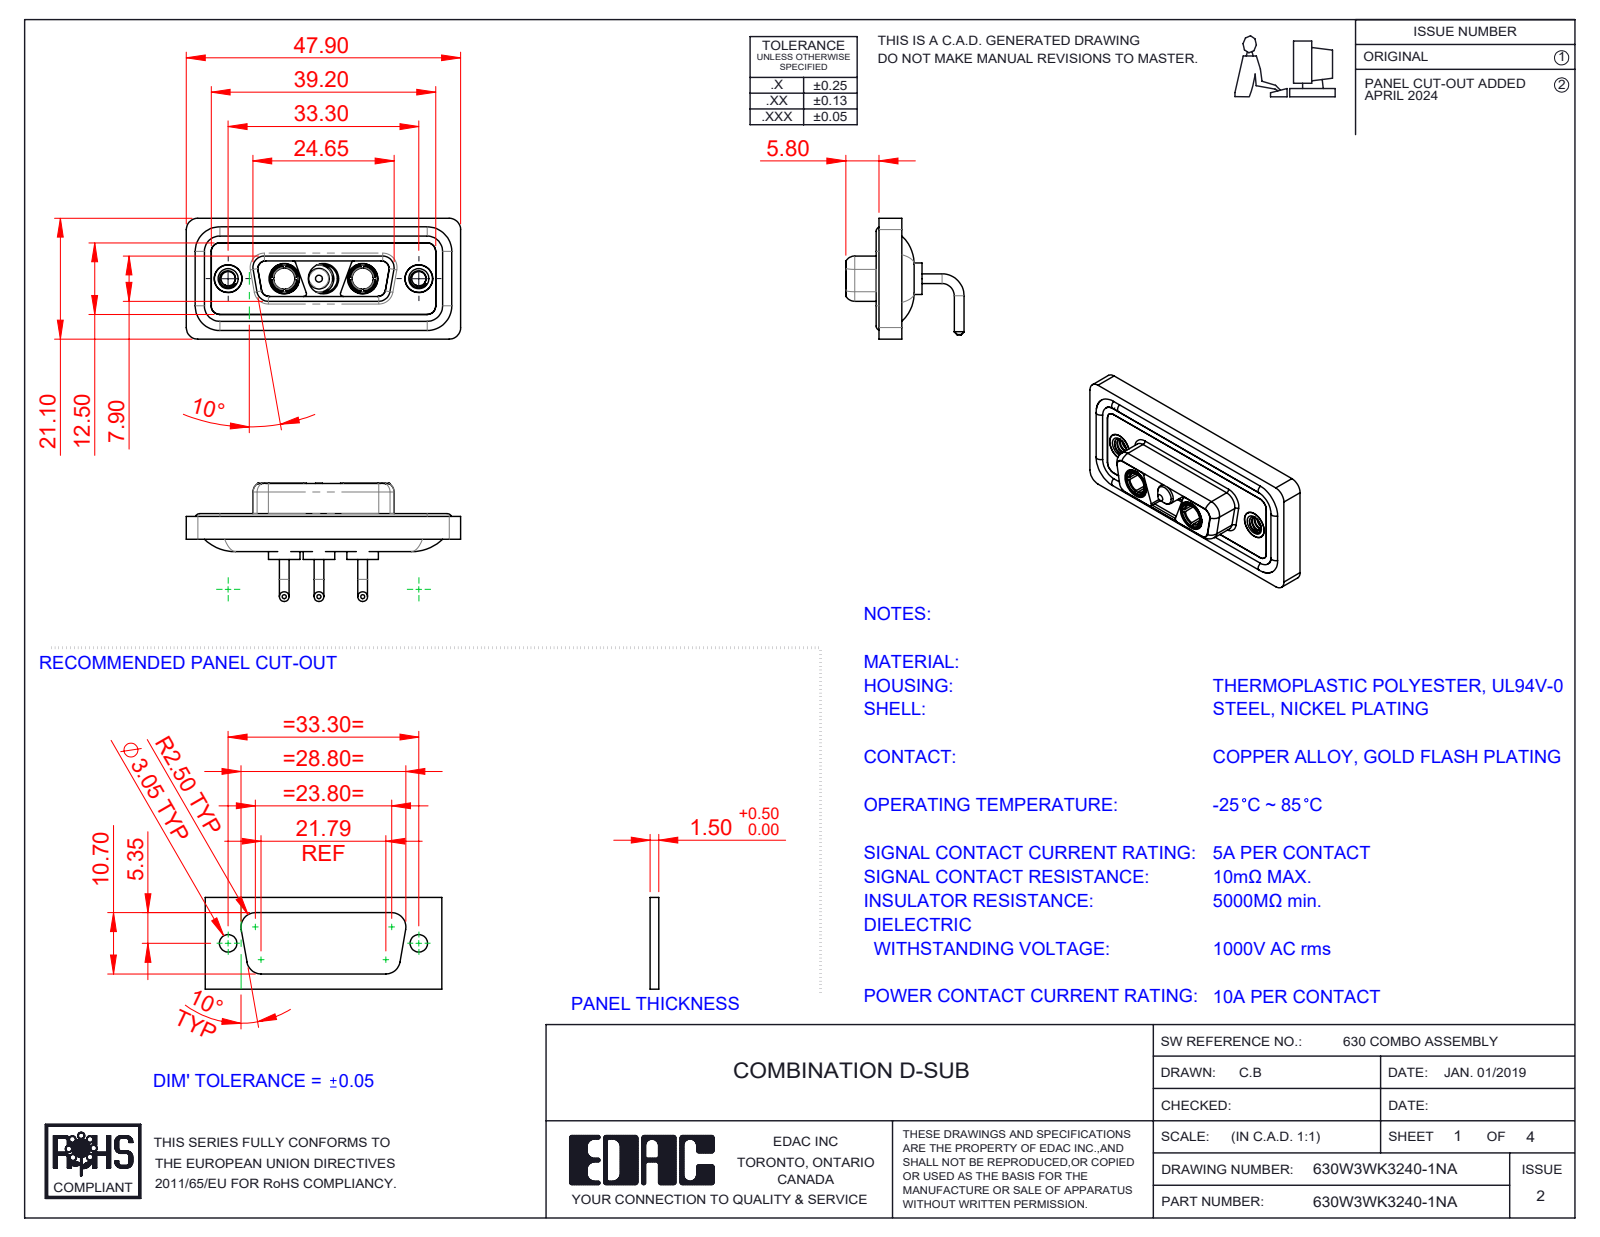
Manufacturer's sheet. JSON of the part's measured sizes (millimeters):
{"part_name": "Power Pin_10A RA; 630W3WK3240-1NA; 630Combo Waterproof Housing_15 Contacts; 630Combo Threaded Rivet_A (+4 more)", "step_written_by": "SolidWorks 2023 (CONFIG_CONTROL_DESIGN)", "units": "millimeters", "bodies": {"solids": 13, "faces": 589, "planar": 178, "cylindrical": 262, "other": 149}, "overall_size": [47.9, 21.1, 20.65], "volume_mm3": 5851, "surface_area_mm2": 9589, "round_holes": [[4.85, 5], [5.3, 3], [2.5, 2], [3.7, 2], [4, 2], [4.05, 2], [5, 2]], "round_bosses_or_shafts": [[1.7, 6], [1.6, 4], [5.5, 3], [5.2, 3], [4.75, 3], [3.75, 3], [4.96, 2], [4.95, 2]], "partial_cylinders_radius": [[2, 20], [1.5, 18], [1.35, 12], [0.5, 8], [1.6, 8], [0.25, 4], [0.6, 4], [0.65, 4]], "face_to_face_distances": [0.4, 1.8, 1.1, 1.6, 2.9, 2.5, 3.1, 3.7, 1.5, 4.1], "hole_center_spacings": [6.85, 9.8, 16.65, 23.5, 13.7, 33.3]}
